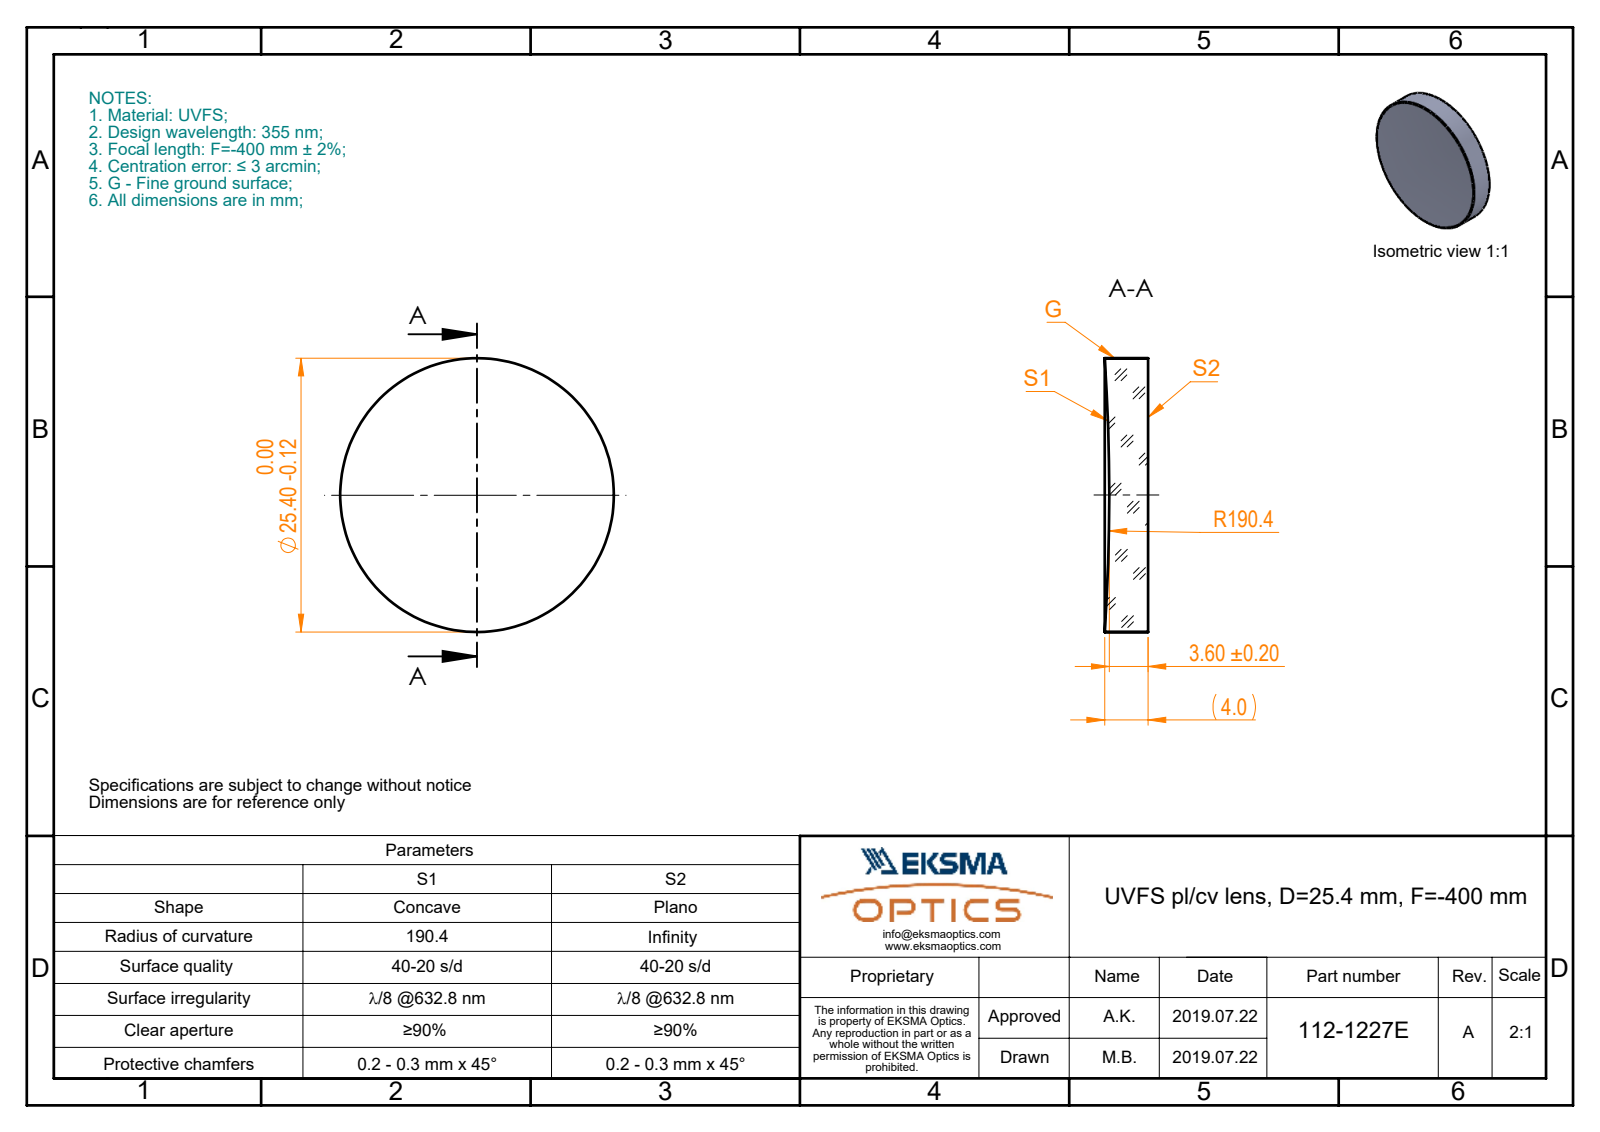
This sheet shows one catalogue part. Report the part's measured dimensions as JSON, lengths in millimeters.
{"part_name": "112-1227E UVFS pl-cv 25.4 F-400", "step_written_by": "SolidWorks 2017 (CONFIG_CONTROL_DESIGN)", "units": "millimeters", "bodies": {"solids": 1, "faces": 5, "planar": 1, "cylindrical": 2, "other": 2}, "overall_size": [25.4, 25.4, 4.02], "volume_mm3": 1932, "surface_area_mm2": 1335, "round_bosses_or_shafts": [[25.4, 1]]}
